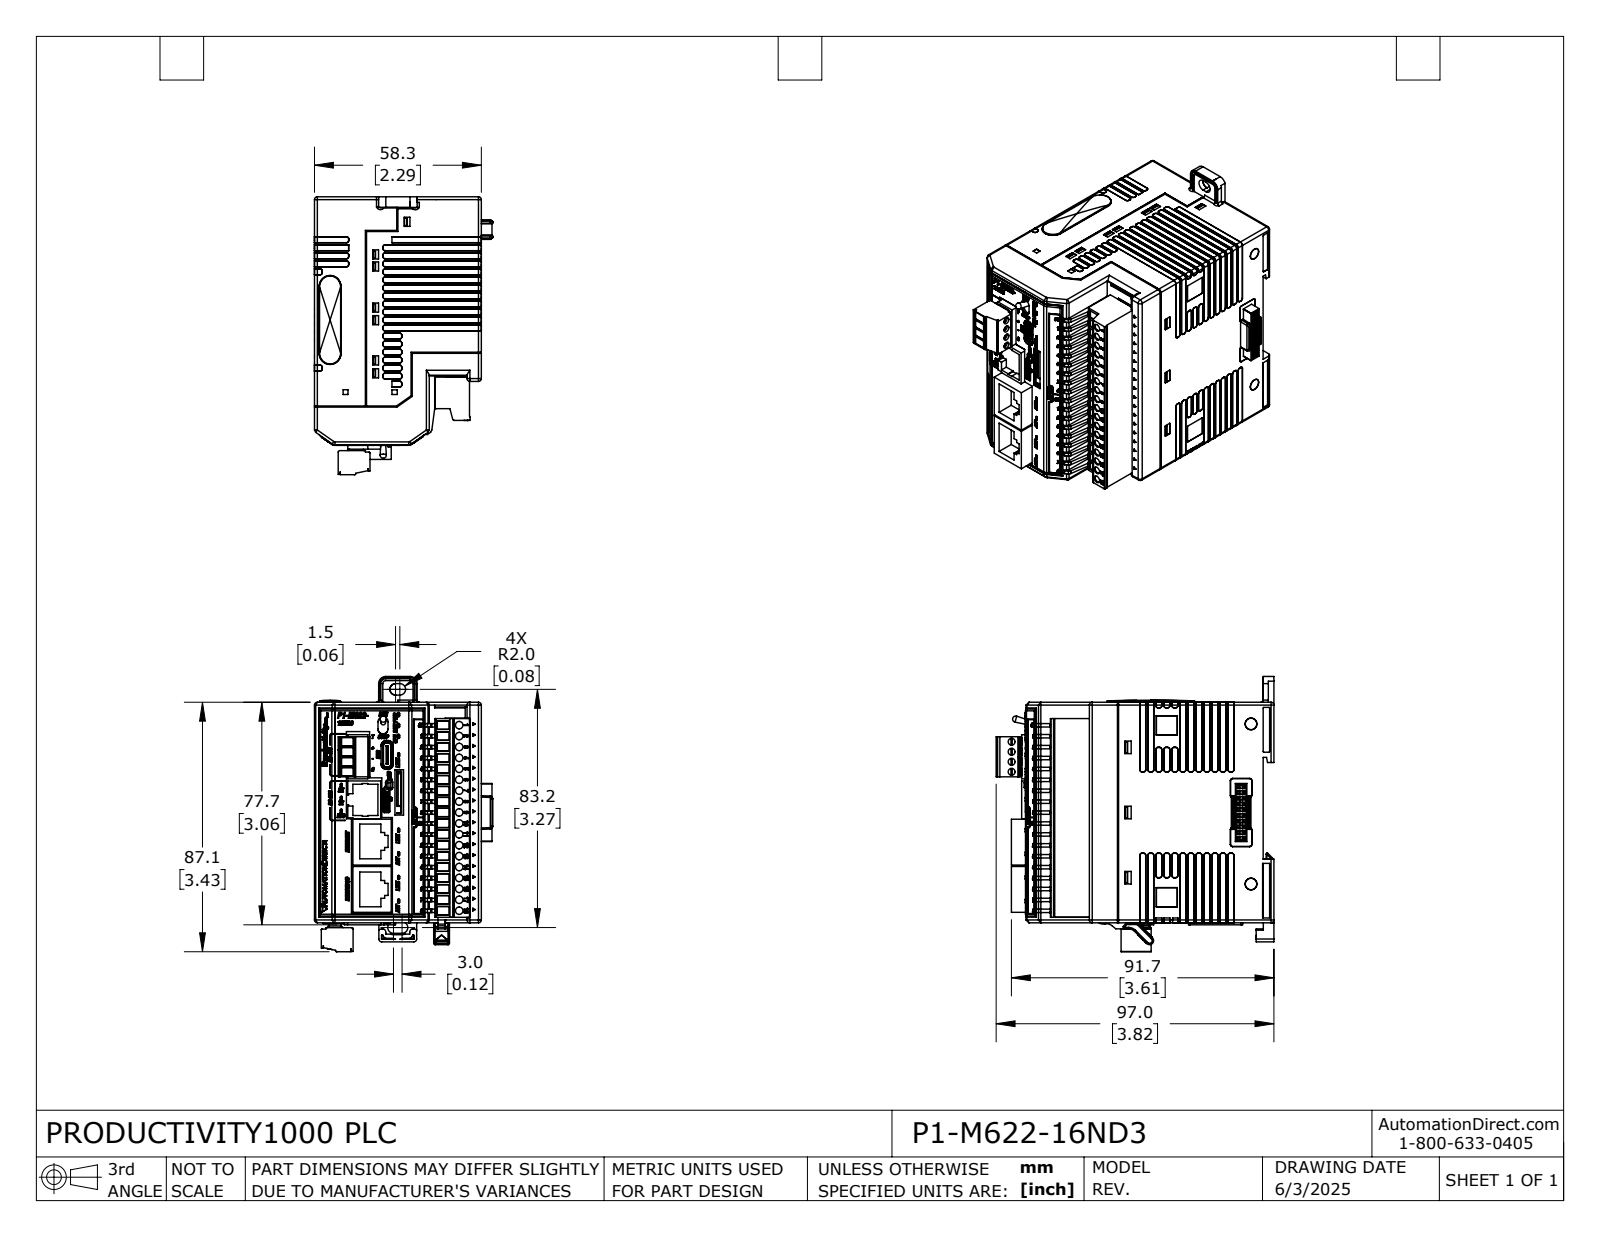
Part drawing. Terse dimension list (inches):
name: P1-M622-16ND3
written by: SolidWorks 2024 (AUTOMOTIVE_DESIGN)
unit: in
bodies: 12 solids, 3652 faces (2072 planar, 886 cylindrical, 694 other)
size: 3.686 × 3.61 × 2.452
volume: 2.158 in³; area: 118.3 in²
rounds: 186× R0.01, 80× R0.008, 53× R0.02, 33× R0.039, 8× R0.079, 7× R0.024, 7× R0.059, 4× R0.012
face distances: 0.05, 0.02, 2.235, 0.039, 2.275, 3.01, 3.022, 2.294, 3.02, 3.031
